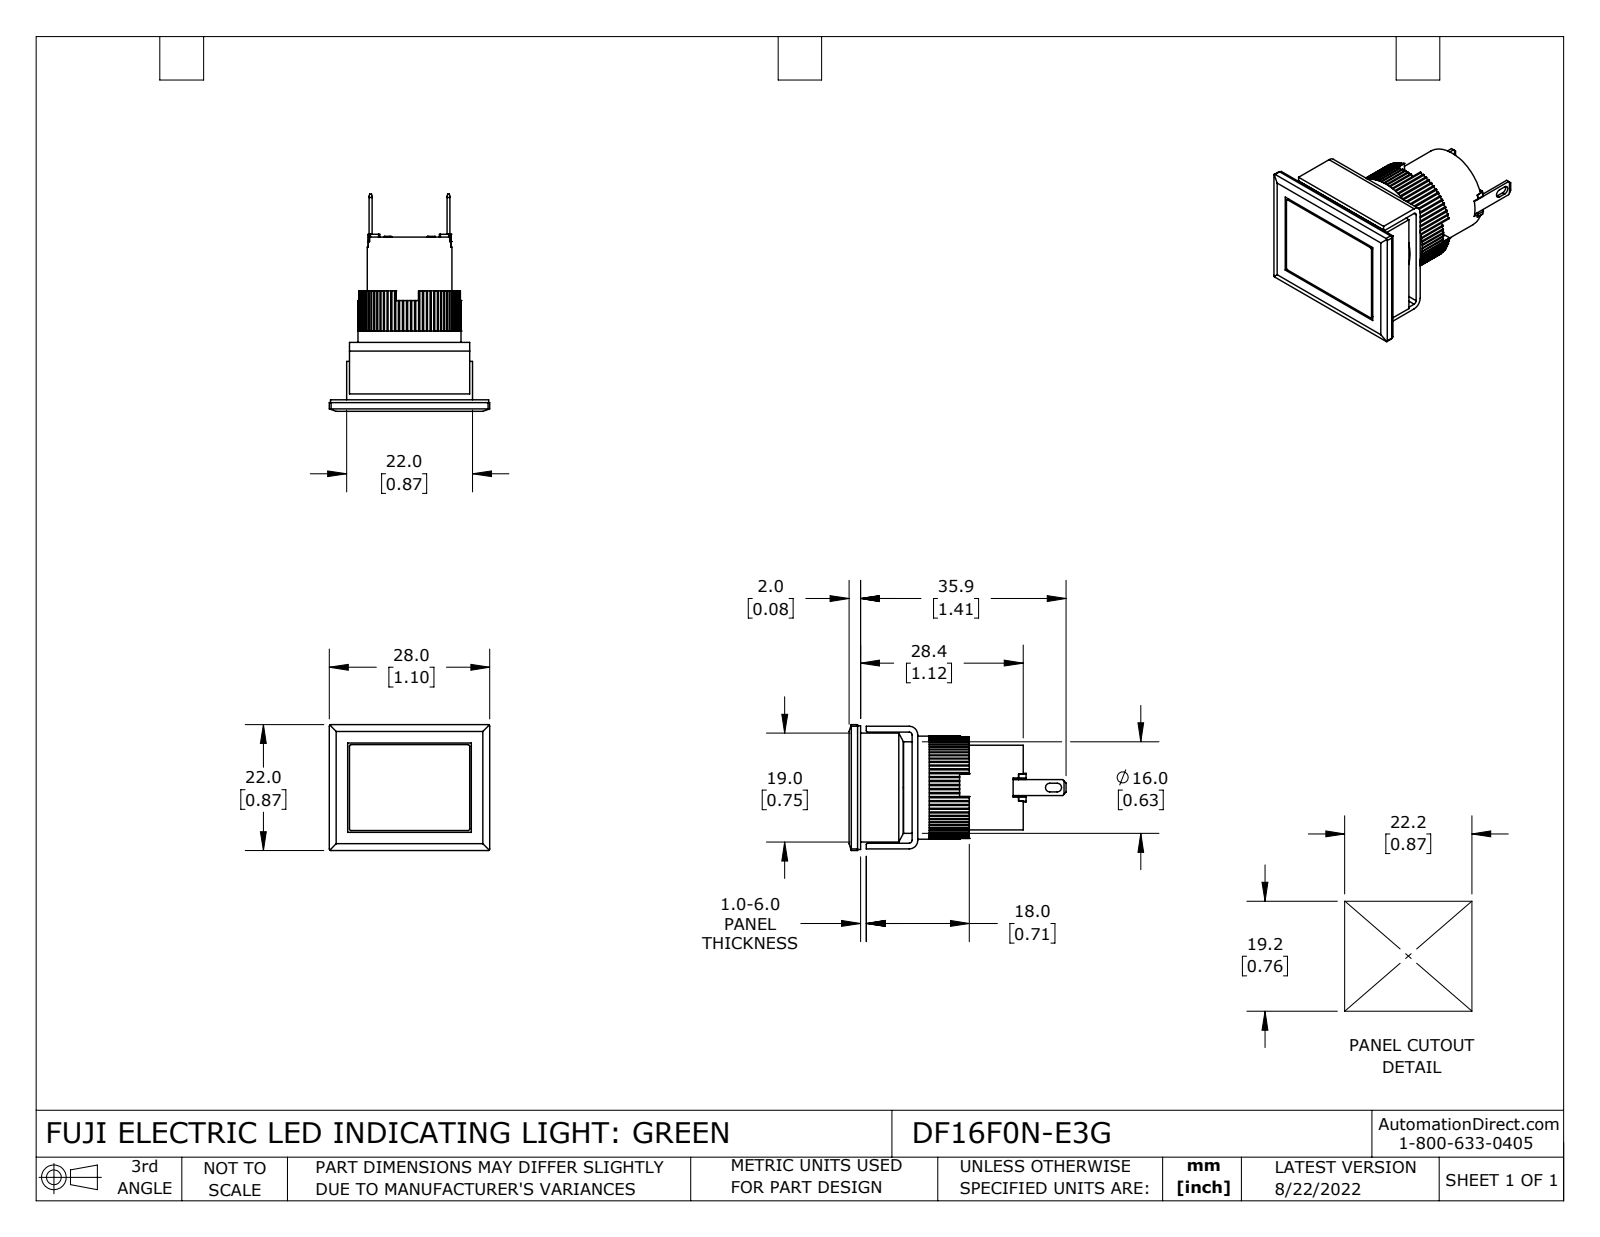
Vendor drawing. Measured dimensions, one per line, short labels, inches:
name: DF16F0N-E3G
written by: SolidWorks 2021 (CONFIG_CONTROL_DESIGN)
unit: in
bodies: 10 solids, 495 faces (312 planar, 181 cylindrical, 2 other)
size: 1.492 × 1.102 × 0.866
volume: 0.546 in³; area: 11.68 in²
holes: 1× ⌀0.039, 1× ⌀0.709
bosses: 1× ⌀0.63, 1× ⌀0.583
rounds: 80× R0.01, 12× R0.008, 8× R0.012, 2× R0.02, 2× R0.03, 2× R0.059
face distances: 0.059, 0.374, 0.142, 0.02, 0.039, 0.315, 0.232, 0.083, 0.079, 0.756
